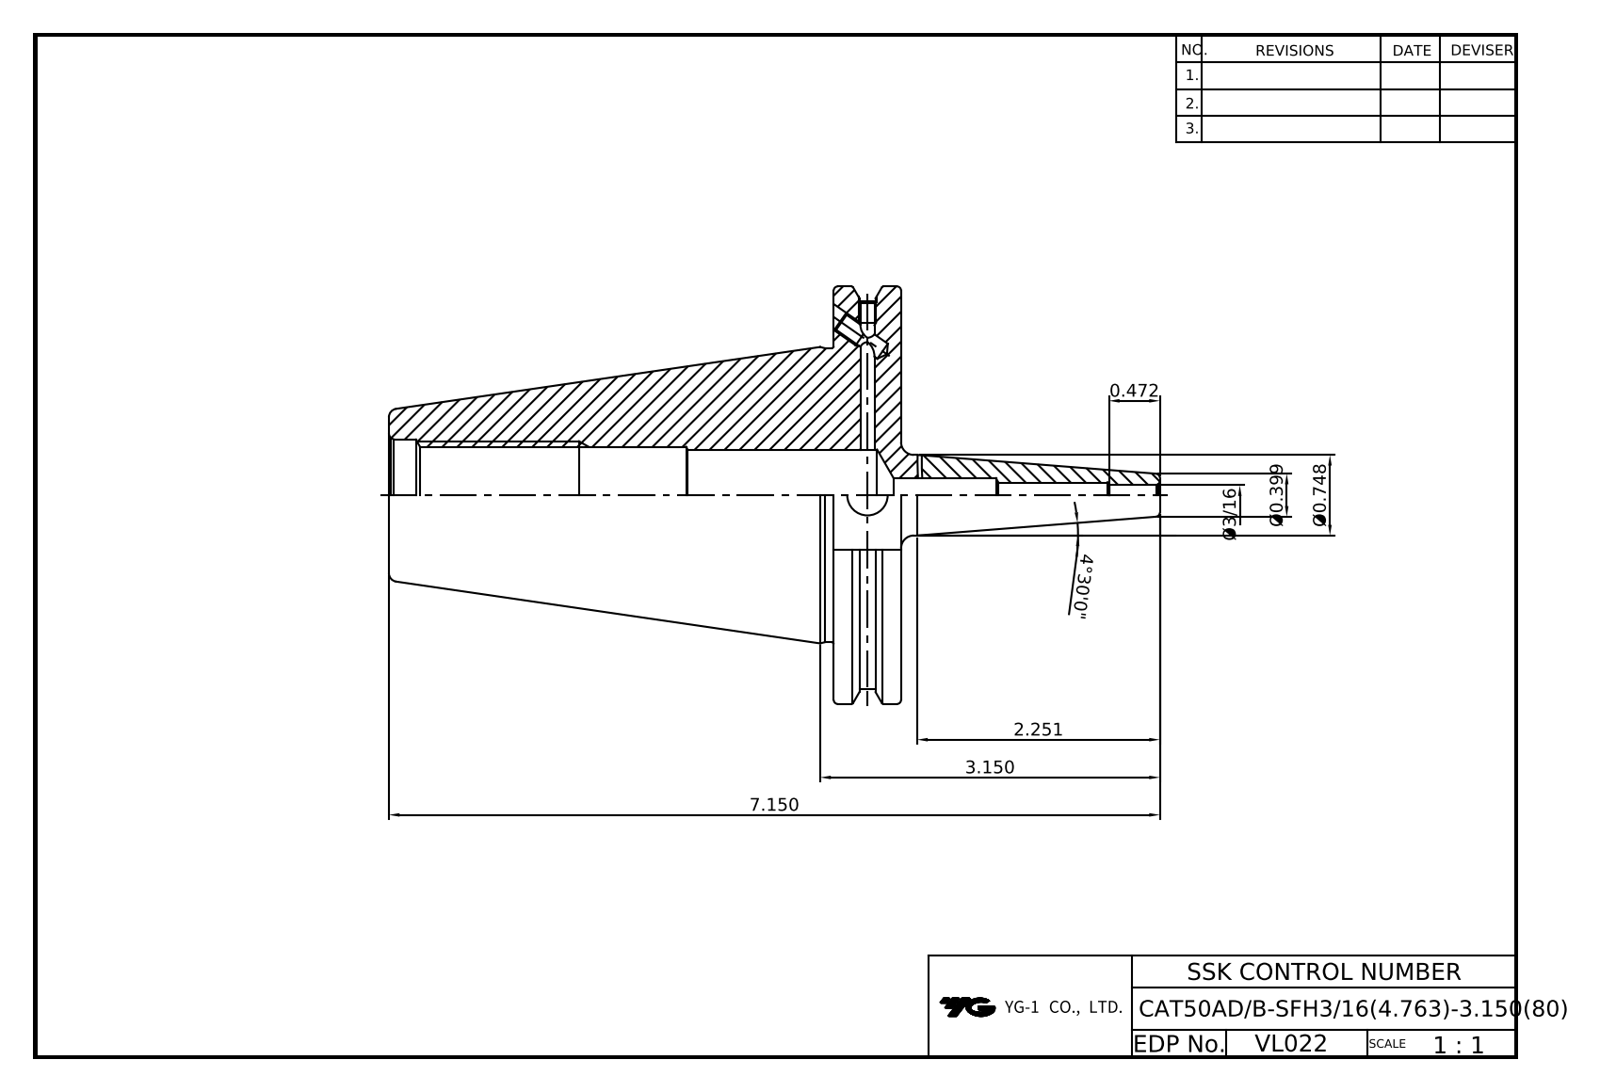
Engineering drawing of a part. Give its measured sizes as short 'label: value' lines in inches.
name: LO-CAT50ADB-SFH4.7625-80
written by: Autodesk Inventor 2025 (AUTOMOTIVE_DESIGN)
unit: in
bodies: 1 solid, 83 faces (35 planar, 26 cylindrical, 22 other)
size: 7.15 × 3.875 × 3.728
volume: 20.21 in³; area: 75.3 in²
holes: 2× ⌀0.128, 2× ⌀0.163, 2× ⌀0.165, 2× ⌀0.197, 1× ⌀0.187, 1× ⌀0.236, 1× ⌀0.315, 1× ⌀0.375, 1× ⌀0.865, 1× ⌀1.031
bosses: 1× ⌀3.875, 1× ⌀3.594, 1× ⌀2.726, 1× ⌀0.748
face distances: 0.625, 4.125, 4.75, 2.875, 1.02, 4.363, 0.238, 0.387, 4.514, 0.389
